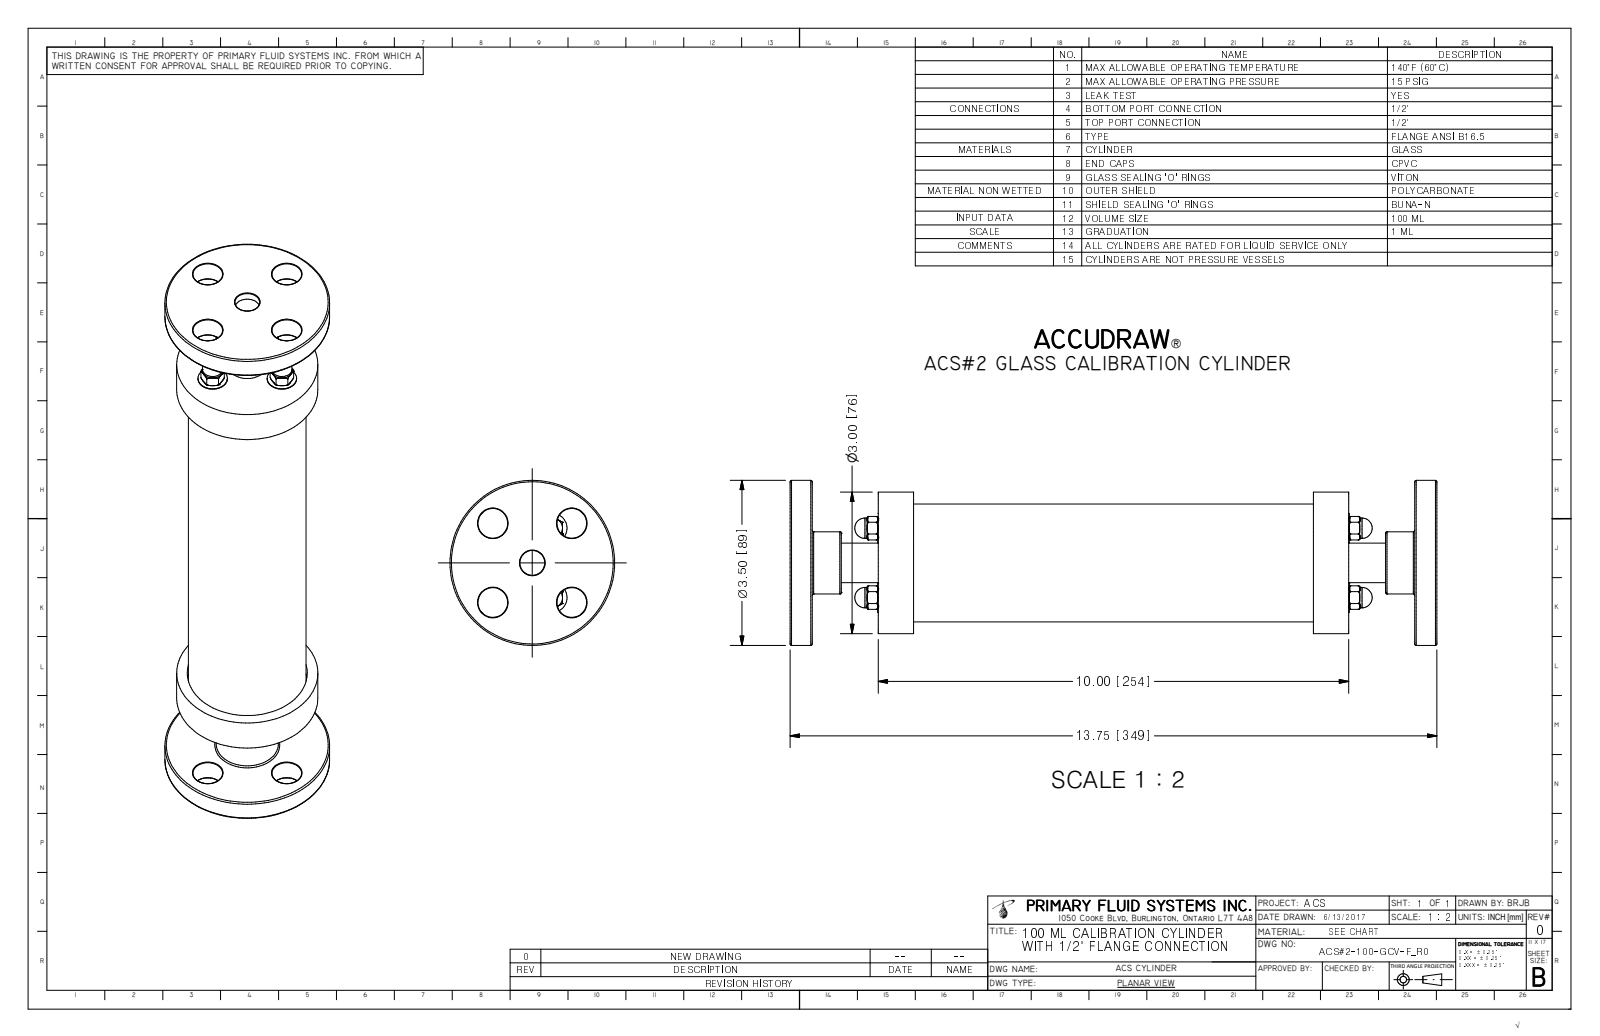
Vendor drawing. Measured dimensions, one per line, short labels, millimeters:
name: ACS#2-100-GCV-F_R0
written by: Autodesk Inventor 2009 (AUTOMOTIVE_DESIGN)
unit: mm
bodies: 1 solid, 494 faces (38 planar, 80 cylindrical, 376 other)
size: 349.3 × 88.9 × 88.9
volume: 621 200 mm³; area: 200 400 mm²
holes: 4× ⌀16, 3× ⌀5.1, 3× ⌀7.1, 1× ⌀13.4, 1× ⌀57.2, 1× ⌀64.8
bosses: 3× ⌀15.9, 3× ⌀4.7, 1× ⌀88.9, 1× ⌀76.2, 1× ⌀63.5, 1× ⌀55.9, 1× ⌀33.5, 1× ⌀30
face distances: 35.7, 289.7, 235, 54.7, 270.6, 19.1, 349.3, 11.9, 337.3, 337.3
hole spacings: 30.2, 42.7, 21.6, 10.9, 21.3, 32.2, 37.4, 41.4
